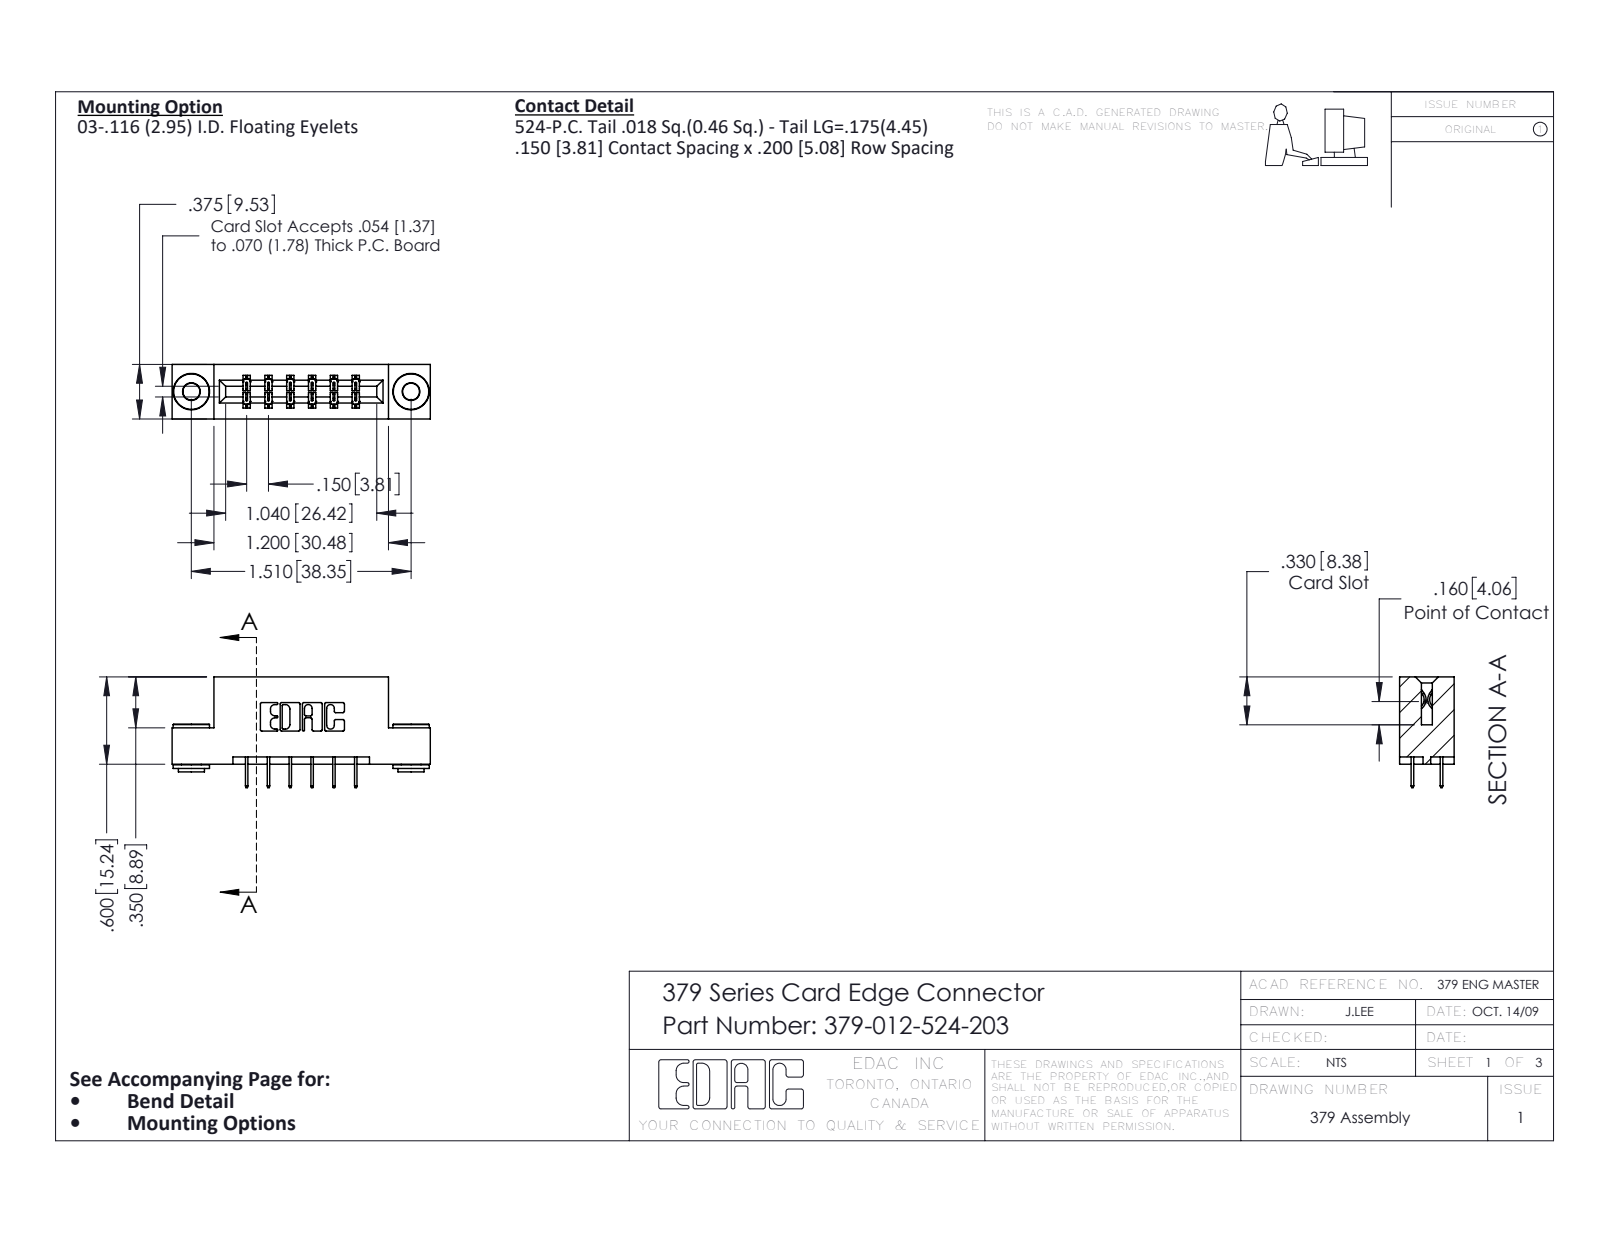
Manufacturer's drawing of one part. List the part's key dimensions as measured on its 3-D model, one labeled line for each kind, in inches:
Part name (STEP PRODUCT): 345-250-002_345-250-002-102; 345-292-001_345-293-124; 379-012-524-203; 379 Part_Flush - .156 Dia - TH
STEP written by: SolidWorks 2016 (CONFIG_CONTROL_DESIGN)
Units: inches
Bodies: 15 solids, 824 faces (584 planar, 232 cylindrical, 8 other)
Overall size (bounding box): 1.775 × 0.762 × 0.375
Volume: 0.265 in³ · Surface area: 7.318 in²
Round holes (diameter × count): ⌀0.116 ×2, ⌀0.156 ×2
Round bosses / shafts (diameter × count): ⌀0.25 ×2, ⌀0.18 ×2, ⌀0.136 ×2
Partial cylindrical surfaces — rounded edges, fillets, slot ends (radius × count): R0.01 ×22, R0.006 ×18, R0.007 ×6, R0.031 ×6, R0.026 ×3, R0.014 ×2, R0.022 ×2, R0.024 ×2
Main face-to-face distances: 0.3, 0.2, 0.05, 0.15, 0.375, 0.25, 0.35, 0.1, 0.075, 0.55
Hole centre spacings: 1.51
